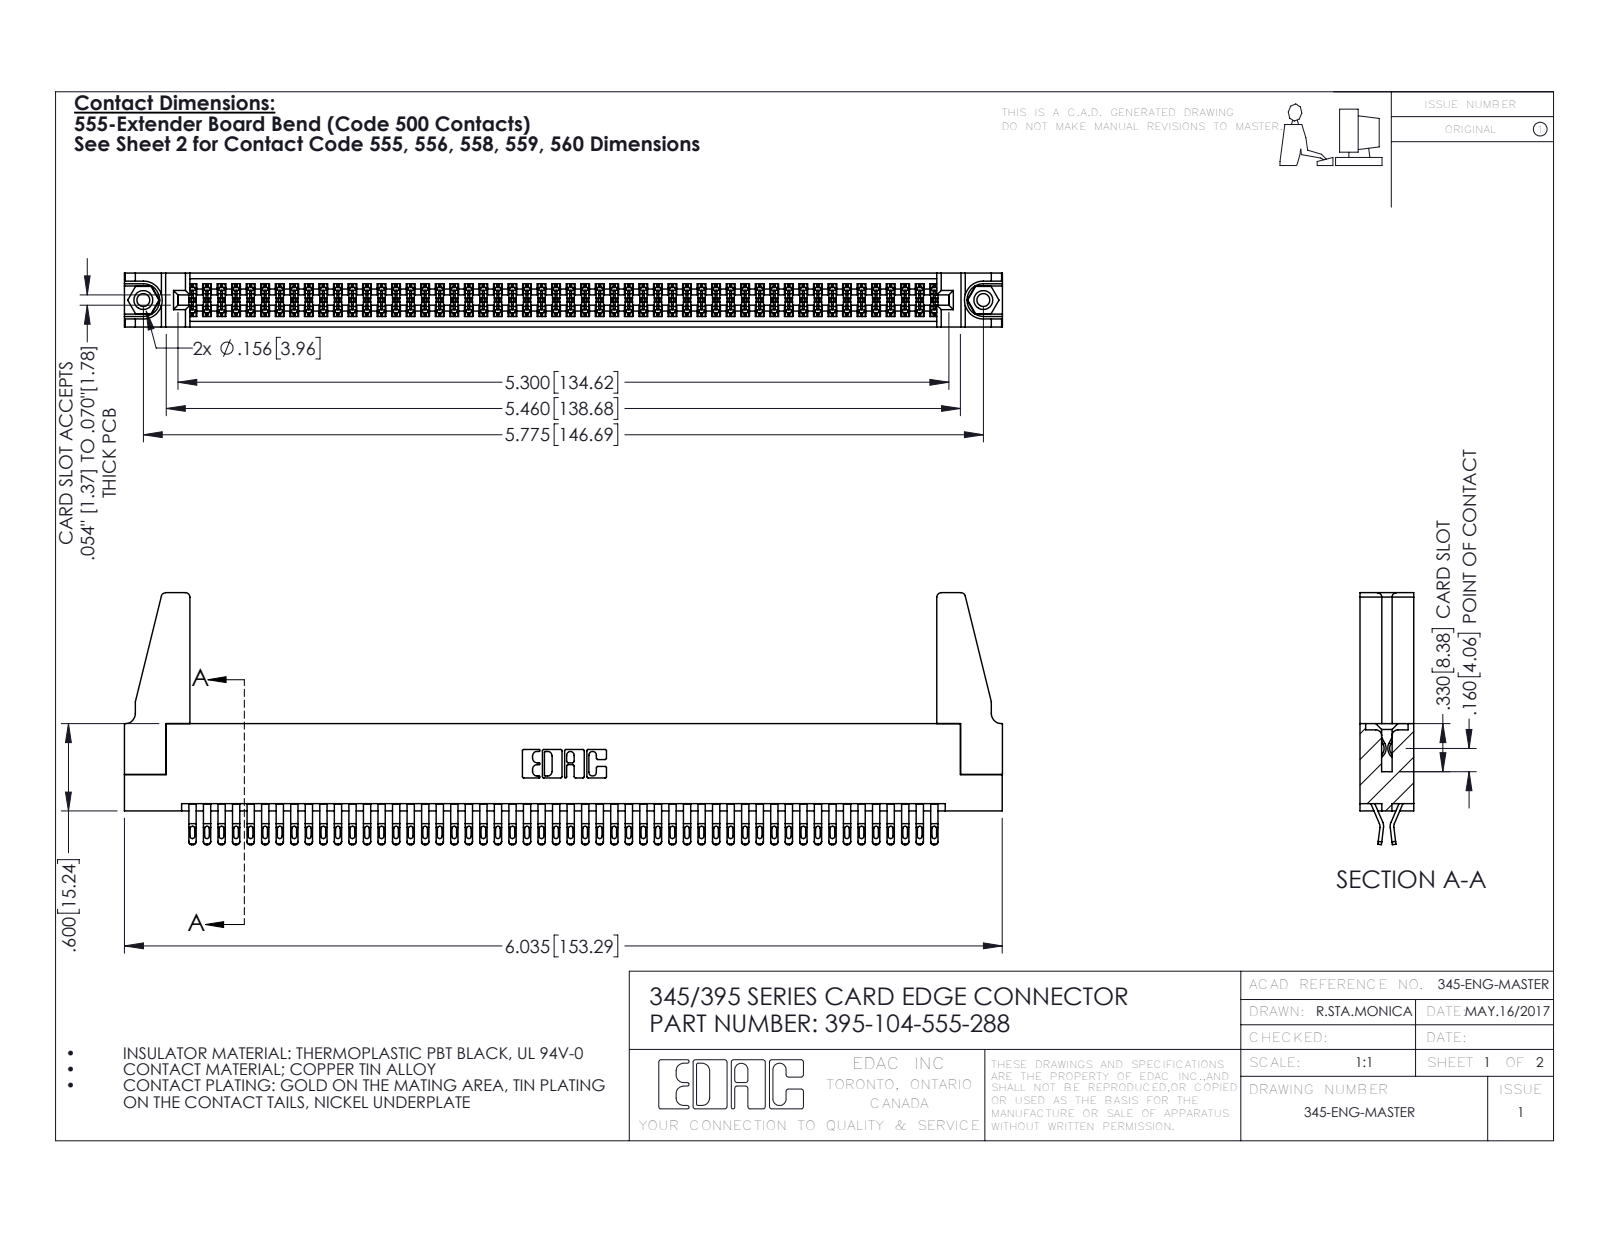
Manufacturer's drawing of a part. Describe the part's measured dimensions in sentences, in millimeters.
The part is named "395-104-555-288; 345-220-078_345-220-088; 345-250-001_345-250-001-102; 345 Part_Flush Mounting Lugs - 0.156 Dia-TH (+1 more)". Its 3-D file was written by "SolidWorks 2016 (CONFIG_CONTROL_DESIGN)". It is 109 solids with 6074 faces: 3376 planar, 2682 cylindrical and 16 other. Overall it measures 153.3 by 44 by 9.4 millimeters. Its volume is 18 530 cubic millimeters and its surface area 26 960 square millimeters. Round holes: 2 of diameter 2.3, 2 of diameter 3.2, 2 of diameter 4, 1 of diameter 1.6. Round bosses or shafts: 2 of diameter 3.9. Partial cylindrical surfaces (rounded edges, fillets, slot ends): 260 of radius 0.4, 208 of radius 0.5, 156 of radius 0.2, 22 of radius 0.3, 8 of radius 0.8, 6 of radius 0.2, 6 of radius 0.8, 3 of radius 0.7. The main face-to-face distances are 1.8, 7.6, 9.4, 0.6, 5.1, 2.5, 6.9, 5.7, 4.4, 3.8. The hole center spacings are 6.9, 140.7, 146.7.
